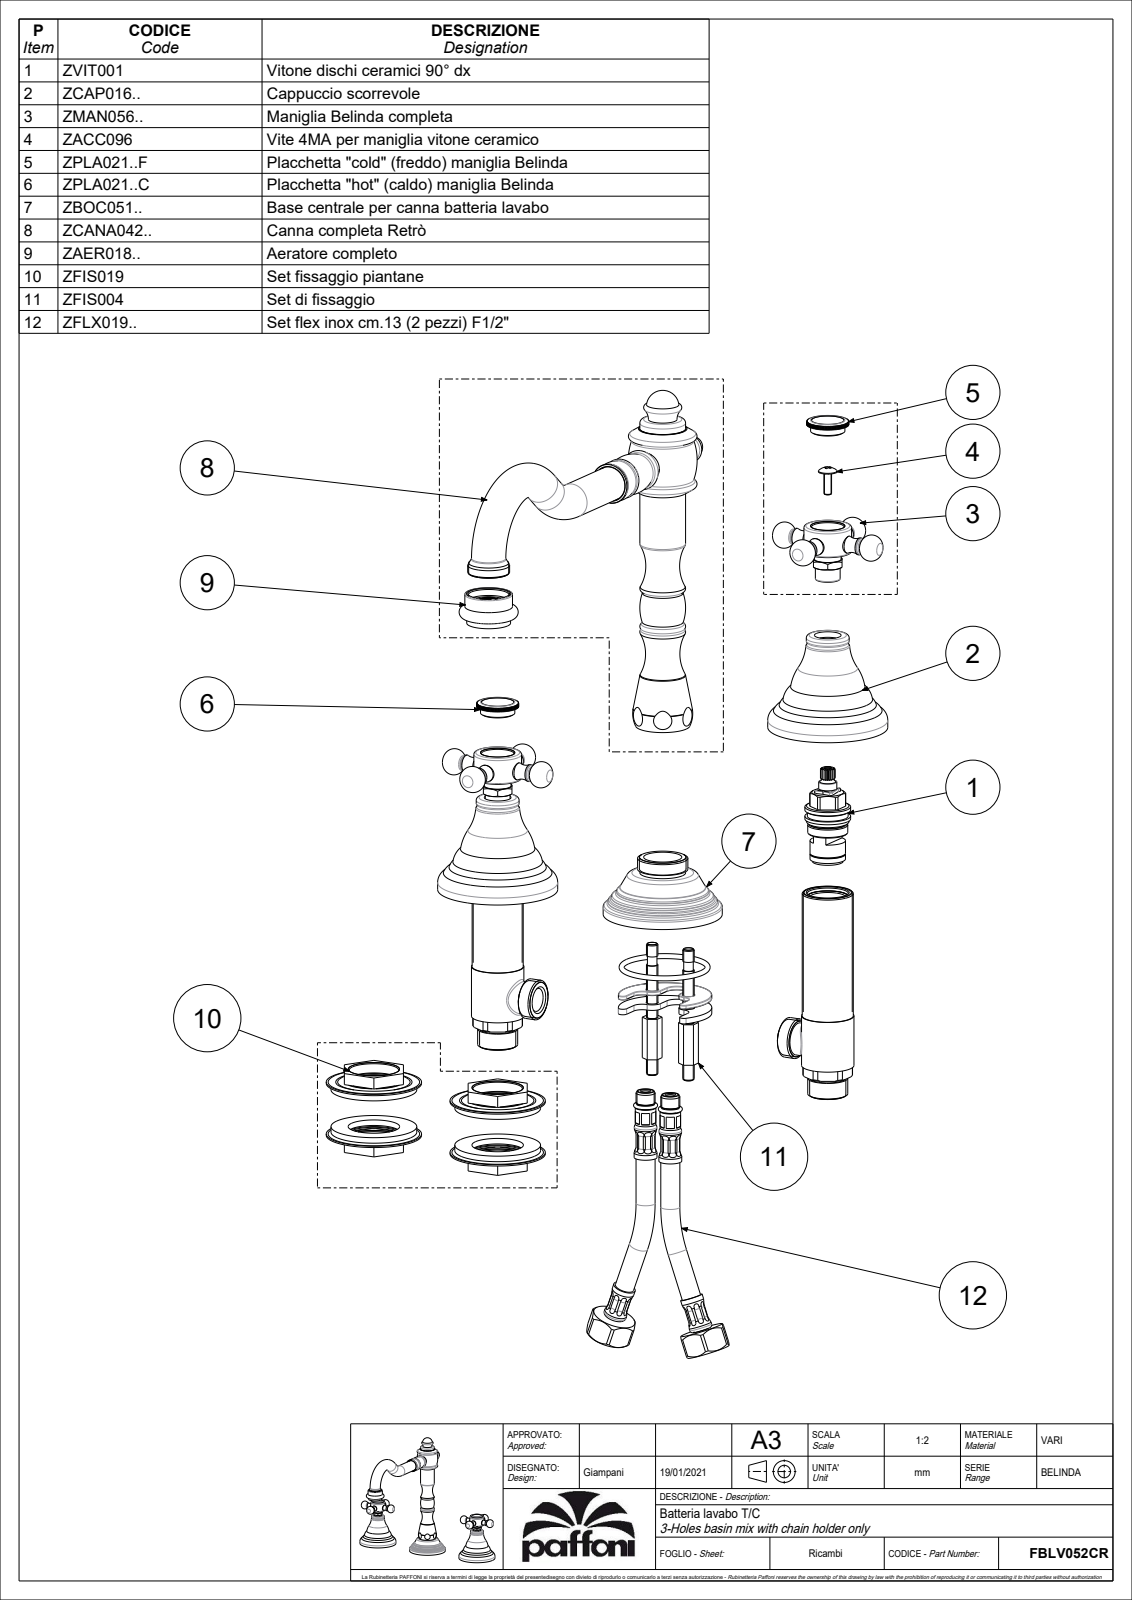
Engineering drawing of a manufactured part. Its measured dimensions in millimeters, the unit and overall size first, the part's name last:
Units: millimetres
Overall size (bounding box): 264.07 × 234.73 × 204.4
Round holes (diameter × count): ⌀5 ×2, ⌀9 ×2, ⌀10 ×2, ⌀11 ×2, ⌀20 ×1, ⌀24.1 ×1, ⌀48.5 ×1
Round bosses / shafts (diameter × count): ⌀25 ×3, ⌀9 ×3, ⌀7 ×3, ⌀63 ×2, ⌀22.5 ×2, ⌀18 ×2, ⌀14 ×2, ⌀13 ×2
Partial cylindrical surfaces — rounded edges, fillets, slot ends (radius × count): R11 ×2
Main face-to-face distances: 30, 60.4, 135.6, 75.2, 2, 58.4, 133.6, 28.4, 32, 103.6
Hole centre spacings: 9.01, 13.46, 13.6, 22.61, 15, 22
Volume: 354 120 mm³ · Surface area: 76 782 mm²
Bodies: 3 solids, 1104 faces (460 planar, 320 cylindrical, 324 other)
Part name (STEP PRODUCT): FBLV052CR
STEP written by: CREO PARAMETRIC BY PTC INC, 2020044 (CONFIG_CONTROL_DESIGN)
